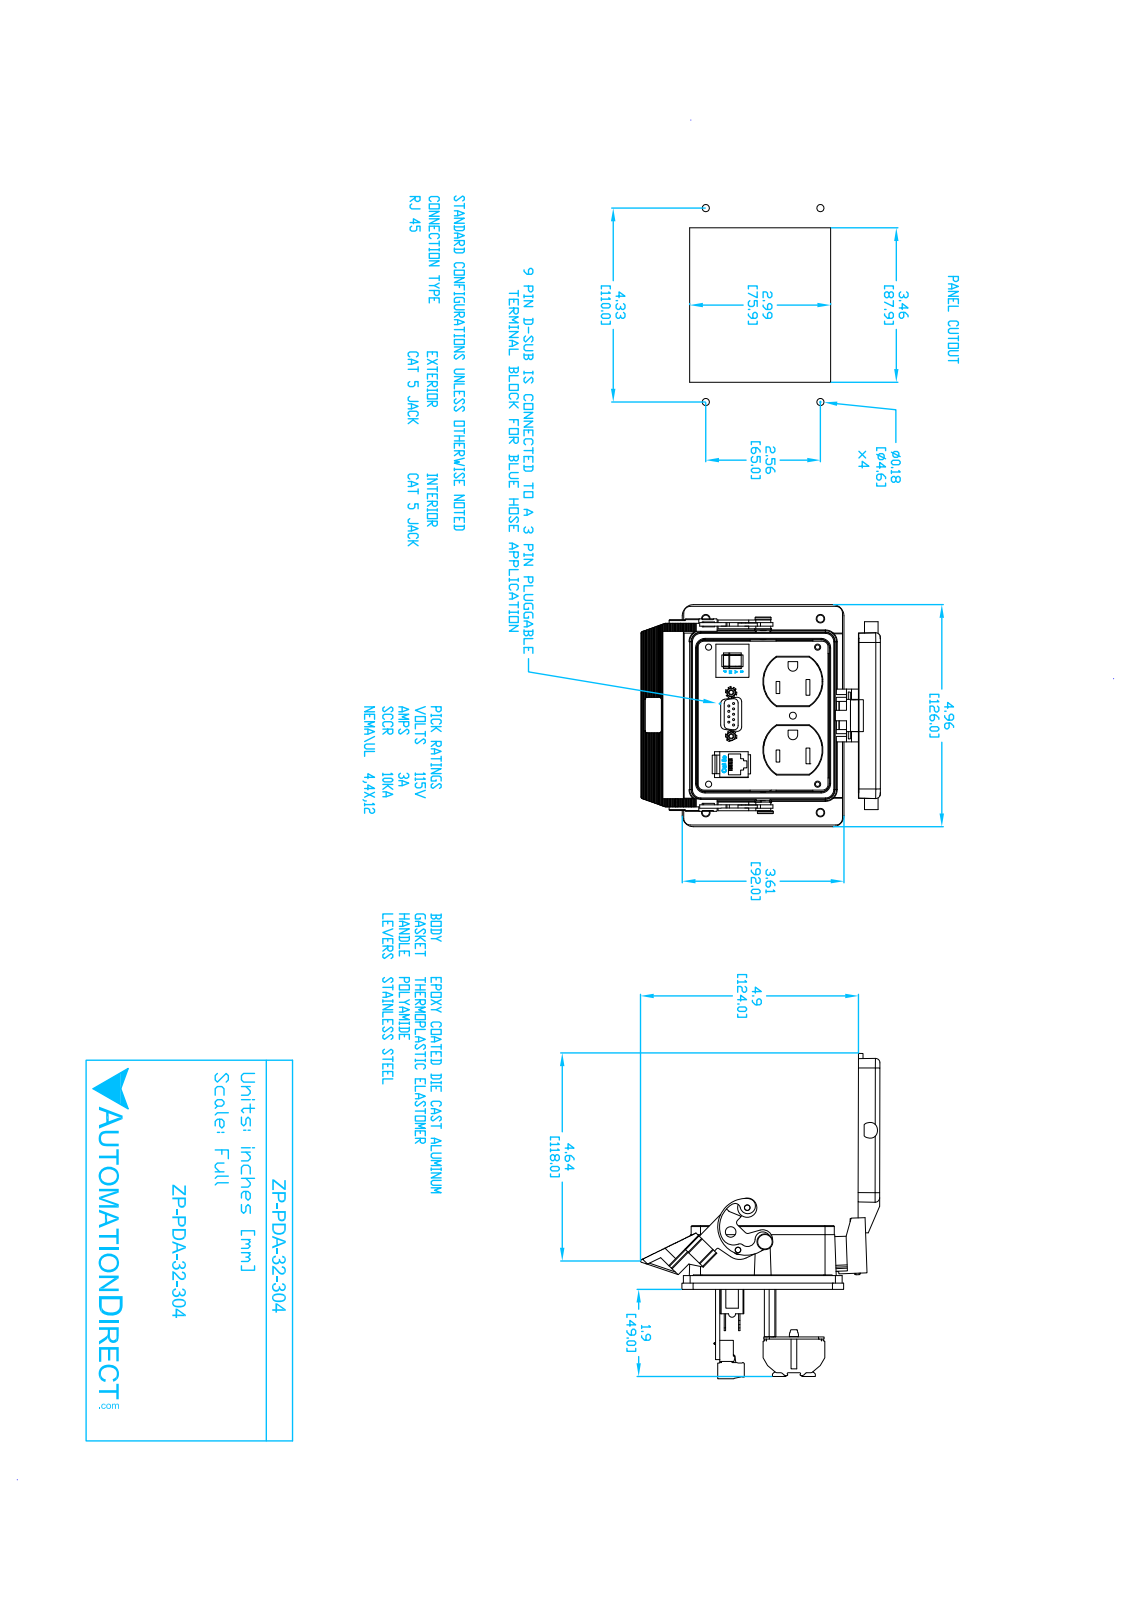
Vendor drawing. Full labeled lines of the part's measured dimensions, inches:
Part name (STEP PRODUCT): ZP-PDA-32-304
STEP written by: SolidWorks 2017 (AUTOMOTIVE_DESIGN)
Units: inches
Bodies: 1 solid, 4483 faces (3004 planar, 796 cylindrical, 683 other)
Overall size (bounding box): 7.305 × 5.313 × 4.96
Volume: 13.92 in³ · Surface area: 205.3 in²
Round holes (diameter × count): ⌀0.038 ×9, ⌀0.045 ×9, ⌀0.098 ×8, ⌀0.144 ×8, ⌀0.16 ×7, ⌀0.173 ×6, ⌀0.073 ×4, ⌀0.19 ×4, ⌀0.05 ×3, ⌀0.091 ×3, ⌀0.118 ×3, ⌀0.125 ×3
Round bosses / shafts (diameter × count): ⌀0.025 ×8, ⌀0.226 ×6, ⌀0.22 ×6, ⌀0.118 ×6, ⌀0.093 ×4, ⌀0.205 ×3, ⌀0.14 ×3, ⌀0.354 ×2
Partial cylindrical surfaces — rounded edges, fillets, slot ends (radius × count): R0.02 ×24, R0.1 ×22, R0.025 ×12, R0.25 ×12, R0.047 ×10, R0.015 ×9, R0.125 ×8, R0.15 ×8
Main face-to-face distances: 0.135, 0.907, 0.847, 0.06, 0.73, 1.577, 1.637, 0.048, 0.778, 1.625
Hole centre spacings: 0.197, 0.12, 0.124, 0.472, 0.108, 0.236, 1.378, 2.578
